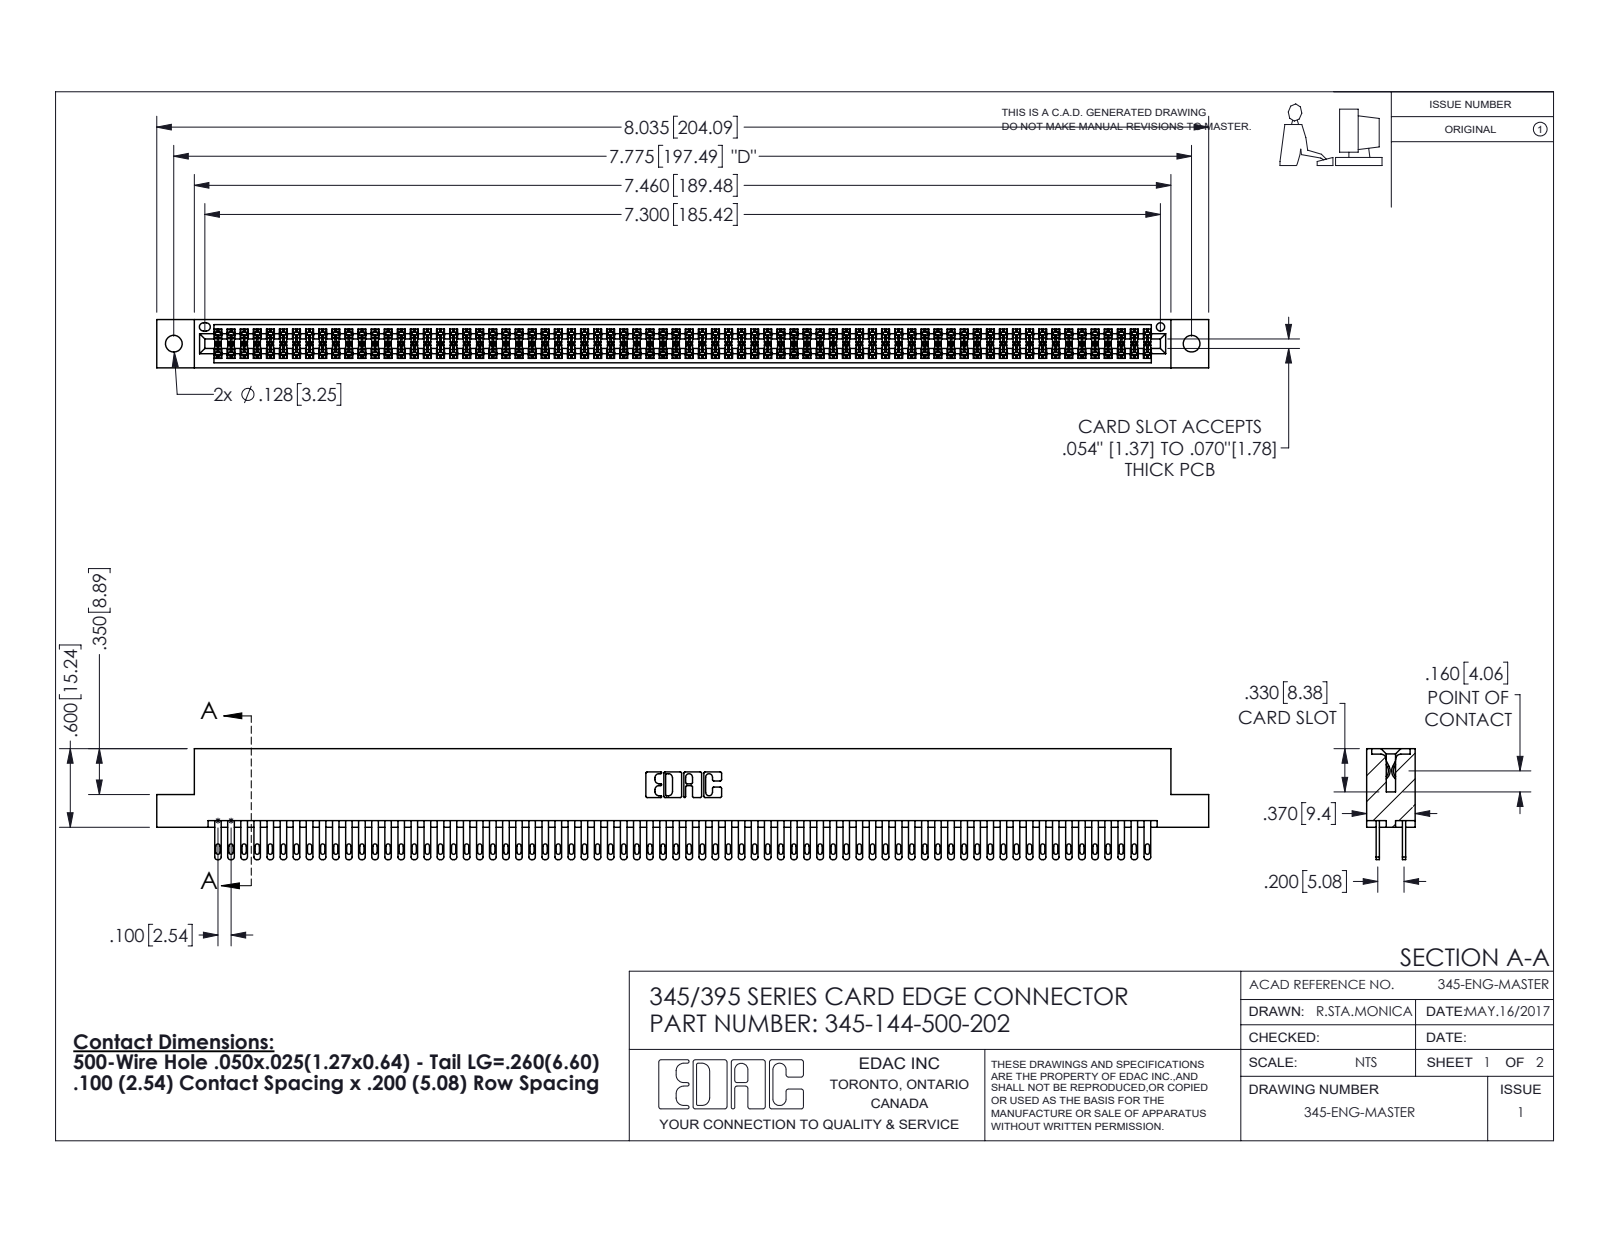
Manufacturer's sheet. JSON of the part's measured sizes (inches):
{"part_name": "345 Part_Flush Mounting Lugs - 0.128 Dia; 345-292-001_345-293-100; 345-144-500-202", "step_written_by": "SolidWorks 2016 (CONFIG_CONTROL_DESIGN)", "units": "inches", "bodies": {"solids": 145, "faces": 6750, "planar": 3968, "cylindrical": 2782, "other": 0}, "overall_size": [8.035, 0.847, 0.37], "volume_in3": 1.251, "surface_area_in2": 49.74, "round_holes": [[0.128, 2], [0.064, 1]], "partial_cylinders_radius": [[0.006, 216], [0.016, 144], [0.02, 144], [0.01, 22], [0.007, 6], [0.031, 6], [0.026, 3], [0.014, 2]], "face_to_face_distances": [0.298, 0.072, 0.2, 0.098, 0.272, 0.025, 0.37, 0.225, 0.175, 0.149], "hole_center_spacings": [0.27, 7.539, 7.775]}
